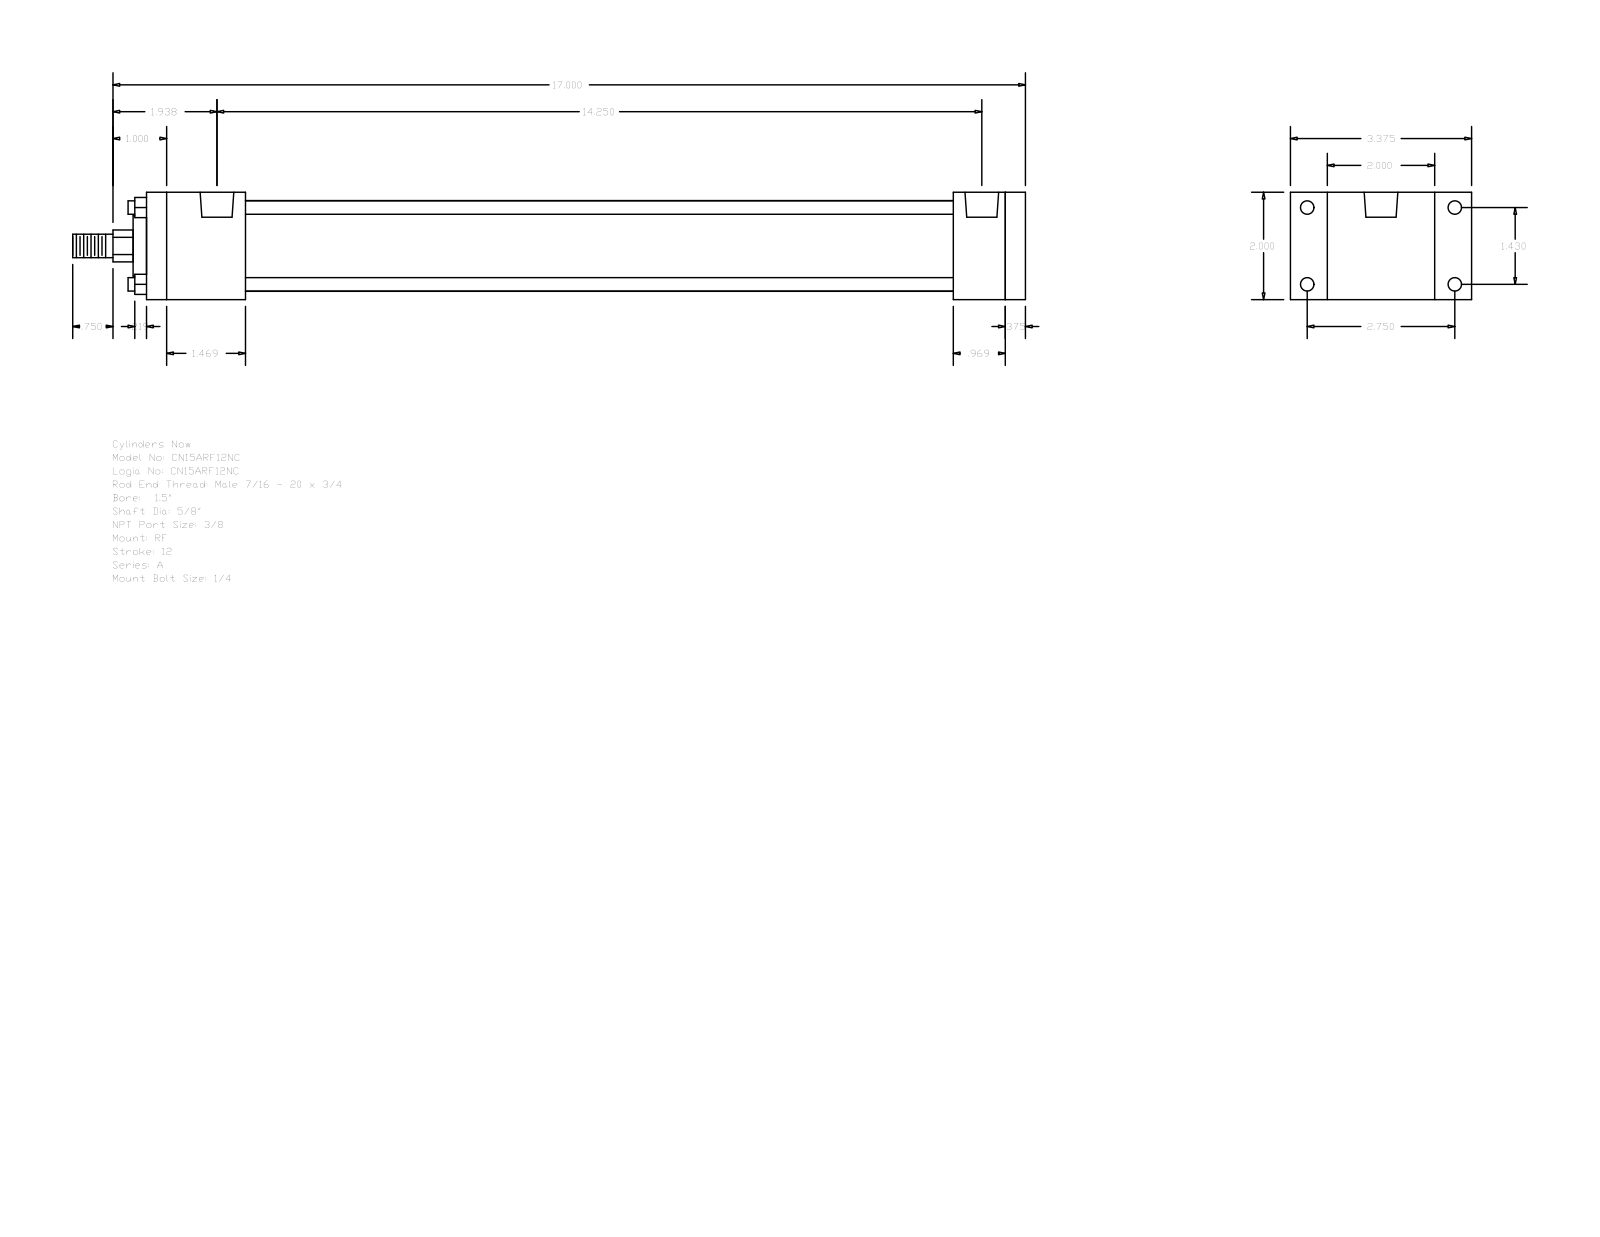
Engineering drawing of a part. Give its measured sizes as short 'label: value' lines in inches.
name: A_RF__0150_0.625
written by: GSSL Pune (CONFIG_CONTROL_DESIGN)
unit: in
bodies: 0 solids, 92 faces (64 planar, 28 cylindrical, 0 other)
size: 17.75 × 3.375 × 2
holes: 4× ⌀0.219, 4× ⌀0.25, 2× ⌀0.627
bosses: 4× ⌀0.25, 1× ⌀1.69, 1× ⌀1.125, 1× ⌀0.625, 1× ⌀0.437
rounds: 1× R0.297
face distances: 2, 0.375, 16.375, 16, 15.031, 0.969, 1.344, 1.844, 13.187, 14.156
hole spacings: 0.156, 1.43, 2.75, 3.099, 13.937, 14.094, 14.25
